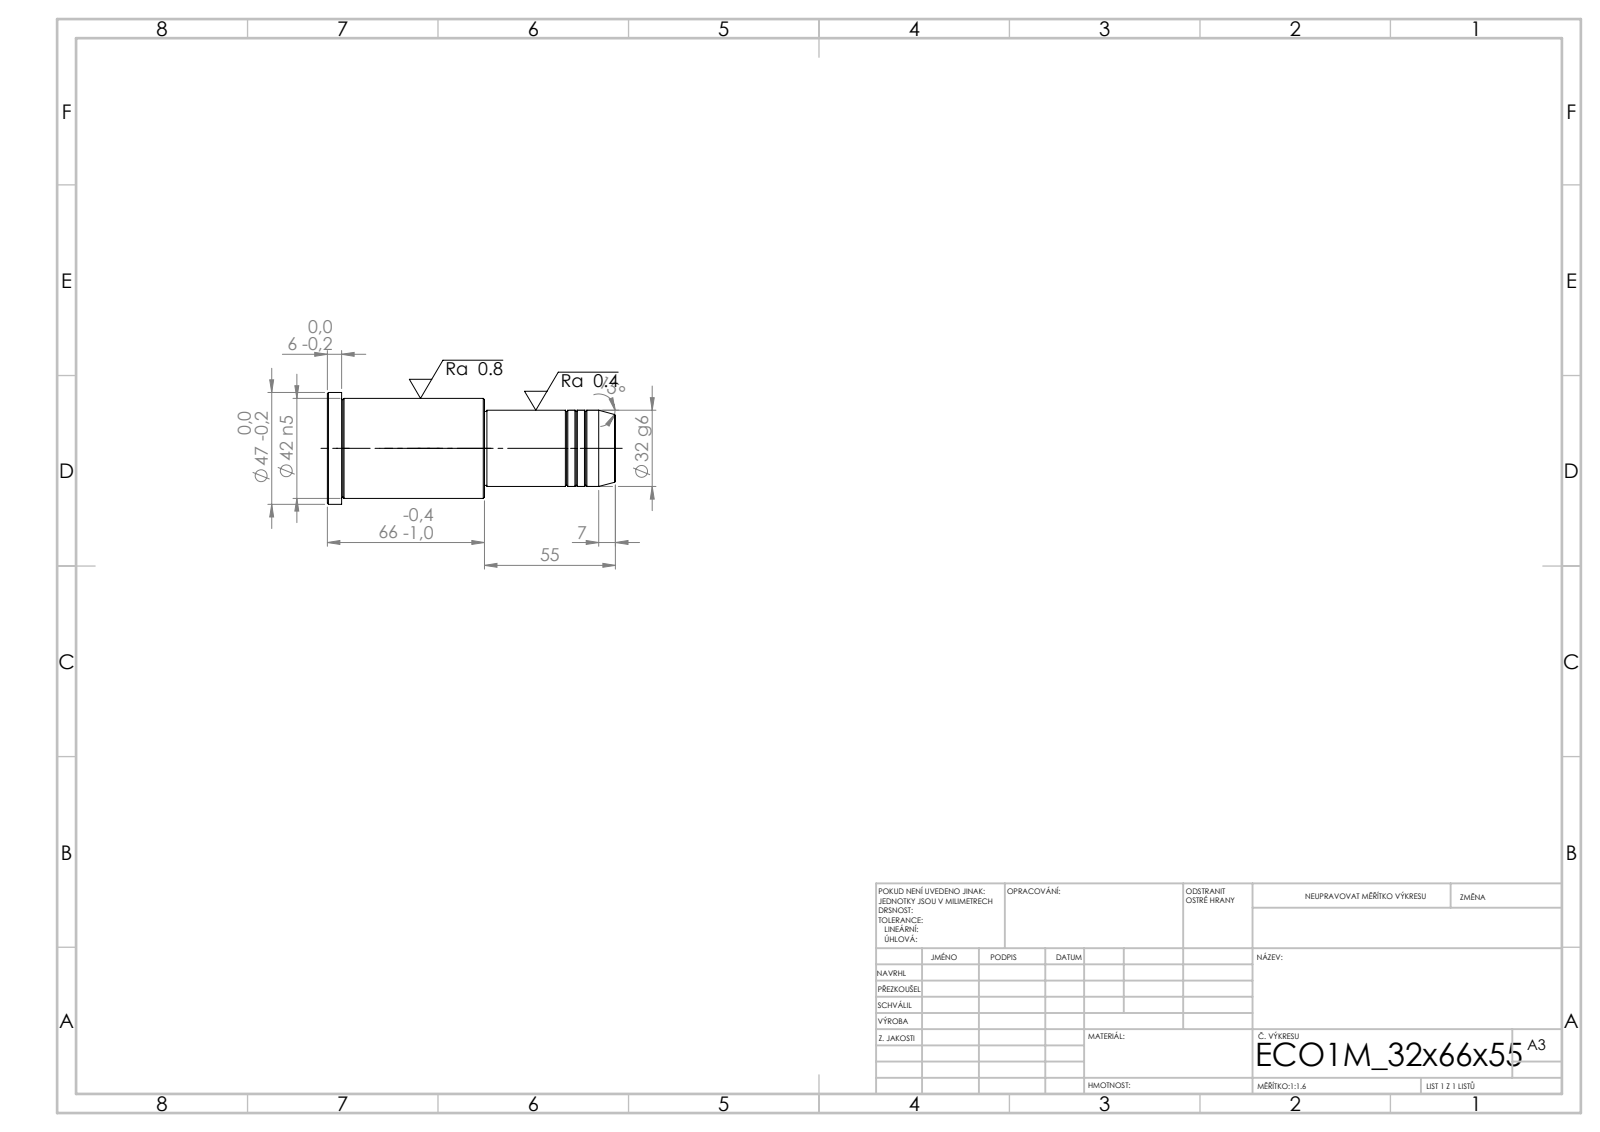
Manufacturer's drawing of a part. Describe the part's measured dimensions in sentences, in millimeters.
Its 3-D file was written by "SolidWorks 2019 (CONFIG_CONTROL_DESIGN)". It is 1 solid with 43 faces: 5 planar, 14 cylindrical and 24 other. Overall it measures 121 by 47 by 47 millimeters. Its volume is 136 881 cubic millimeters and its surface area 17 845 square millimeters. Round bosses or shafts: 1 of diameter 47, 1 of diameter 42, 1 of diameter 32, 1 of diameter 31. The main face-to-face distances are 121, 55, 66, 115, 60, 6, 54, 1, 61, 67.
